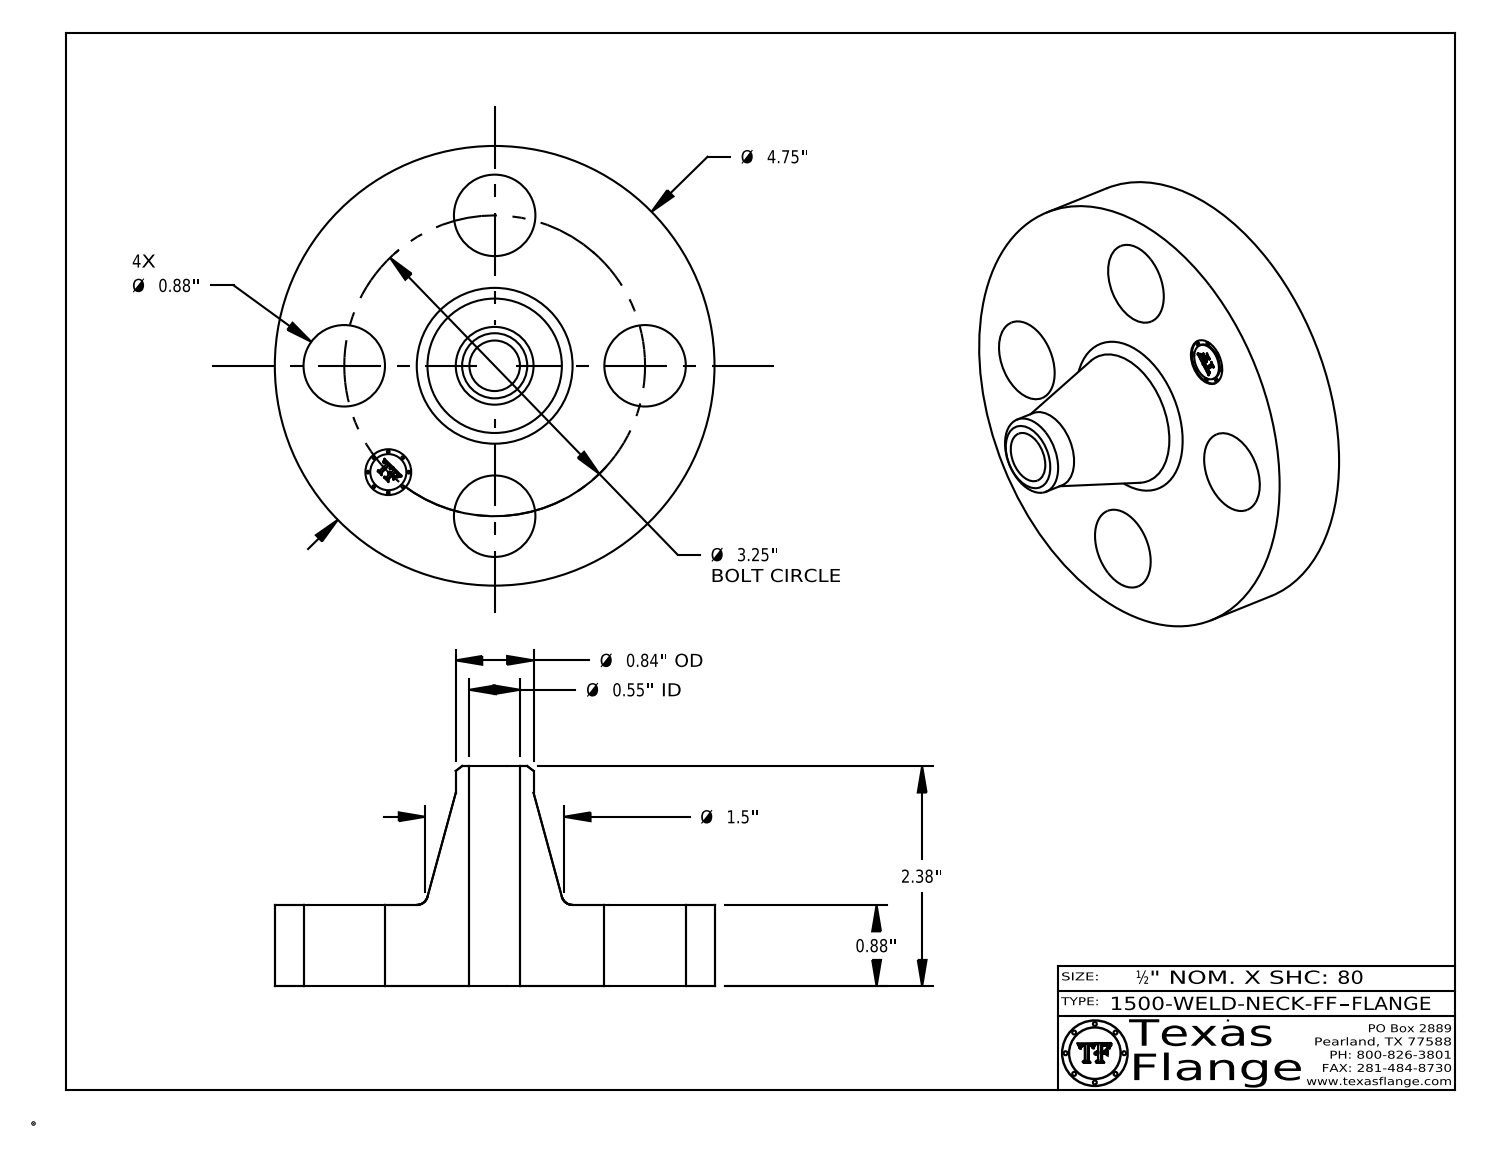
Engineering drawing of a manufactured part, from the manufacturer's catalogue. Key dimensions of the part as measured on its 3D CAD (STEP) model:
Part name (STEP PRODUCT): 1500-WELD-NECK-FF
STEP written by: CATIA V5 STEP AP214 (AUTOMOTIVE_DESIGN)
Units: inches
Bodies: 1 solid, 408 faces (368 planar, 34 cylindrical, 6 other)
Overall size (bounding box): 4.75 × 4.75 × 2.38
Volume: 14.39 in³ · Surface area: 61.09 in²
Round holes (diameter × count): ⌀0.88 ×4, ⌀0.495 ×1, ⌀0.546 ×1
Round bosses / shafts (diameter × count): ⌀0.03 ×8, ⌀4.75 ×1, ⌀0.84 ×1, ⌀0.39 ×1
Main face-to-face distances: 0.88, 2.38, 1.5, 0.865, 0.015, 1.515, 0.148, 0.144, 0.027, 0.096
Hole centre spacings: 1.625, 2.298, 1.244, 3.003, 3.25
